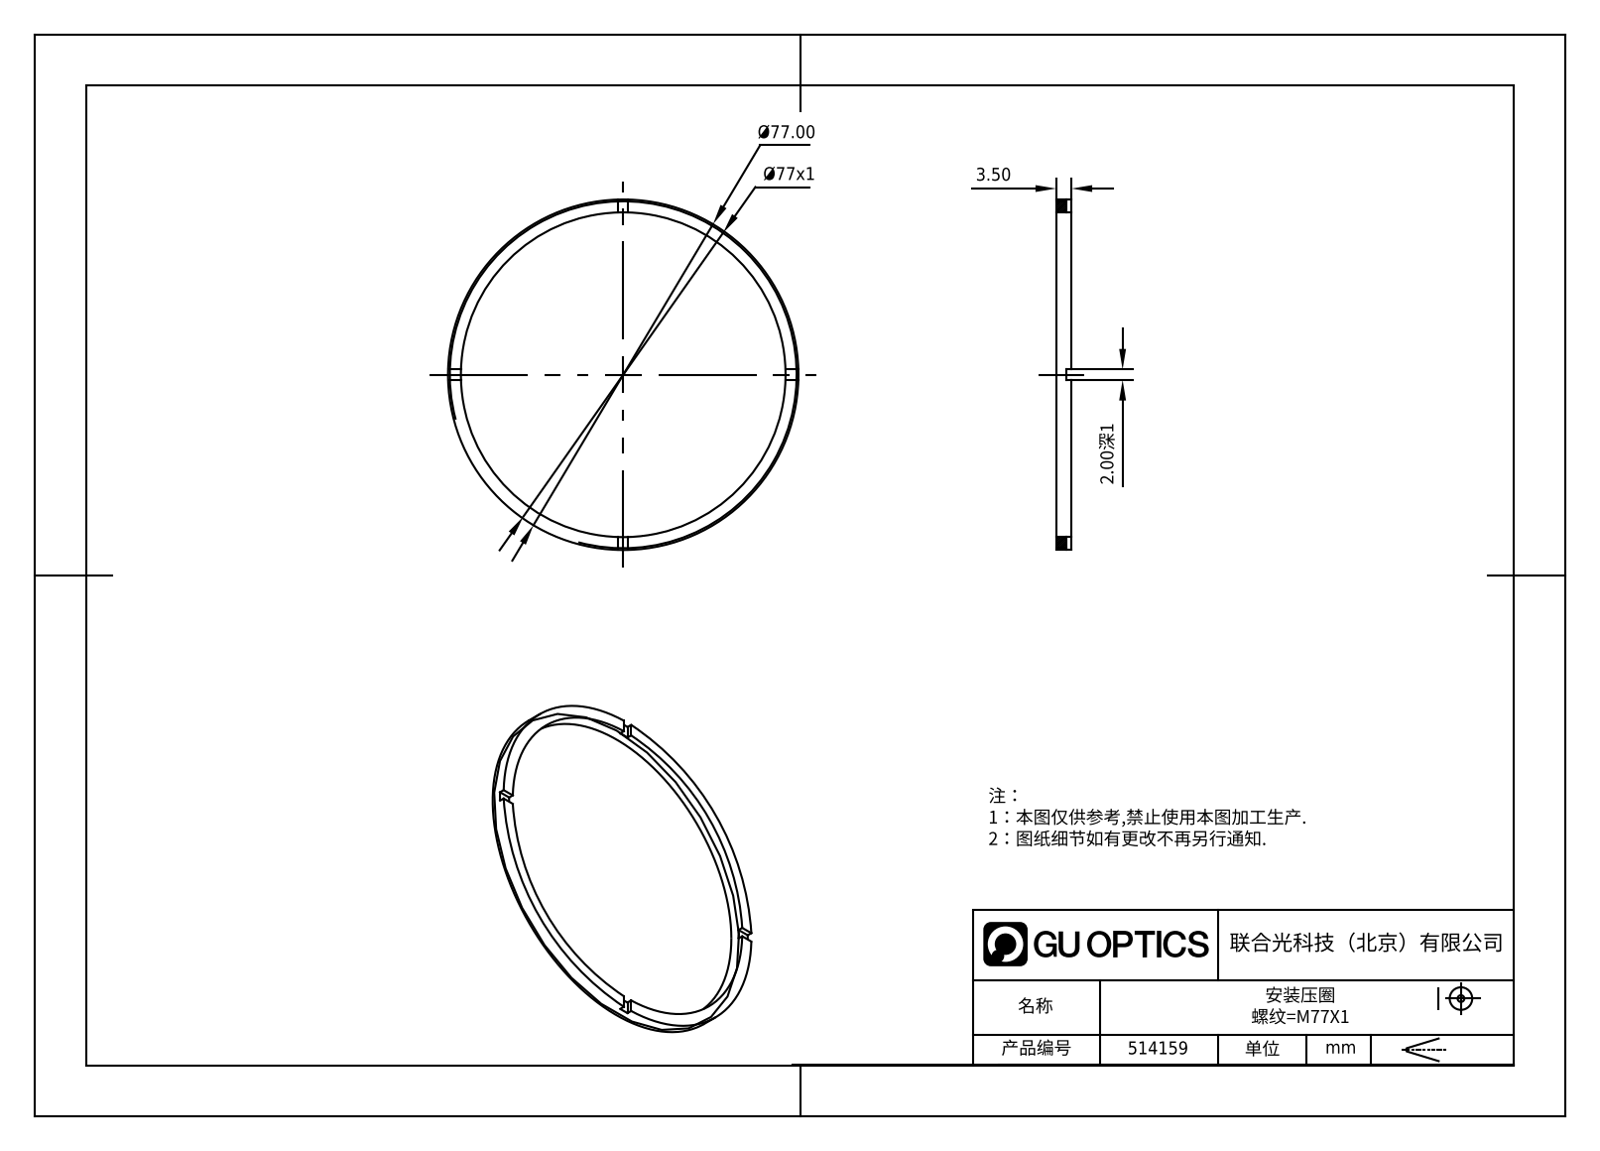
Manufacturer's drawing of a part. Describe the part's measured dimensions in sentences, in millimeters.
The part is named "514159". Its 3-D file was written by "SolidWorks 2020 (CONFIG_CONTROL_DESIGN)". It is 1 solid with 21 faces: 17 planar, 4 cylindrical and 0 other. Overall it measures 77 by 77 by 3.5 millimeters. Its volume is 2 417 cubic millimeters and its surface area 3 030 square millimeters. Round holes: 1 of diameter 71. Round bosses or shafts: 1 of diameter 77. The main face-to-face distances are 3.5, 2.5, 1, 2.
